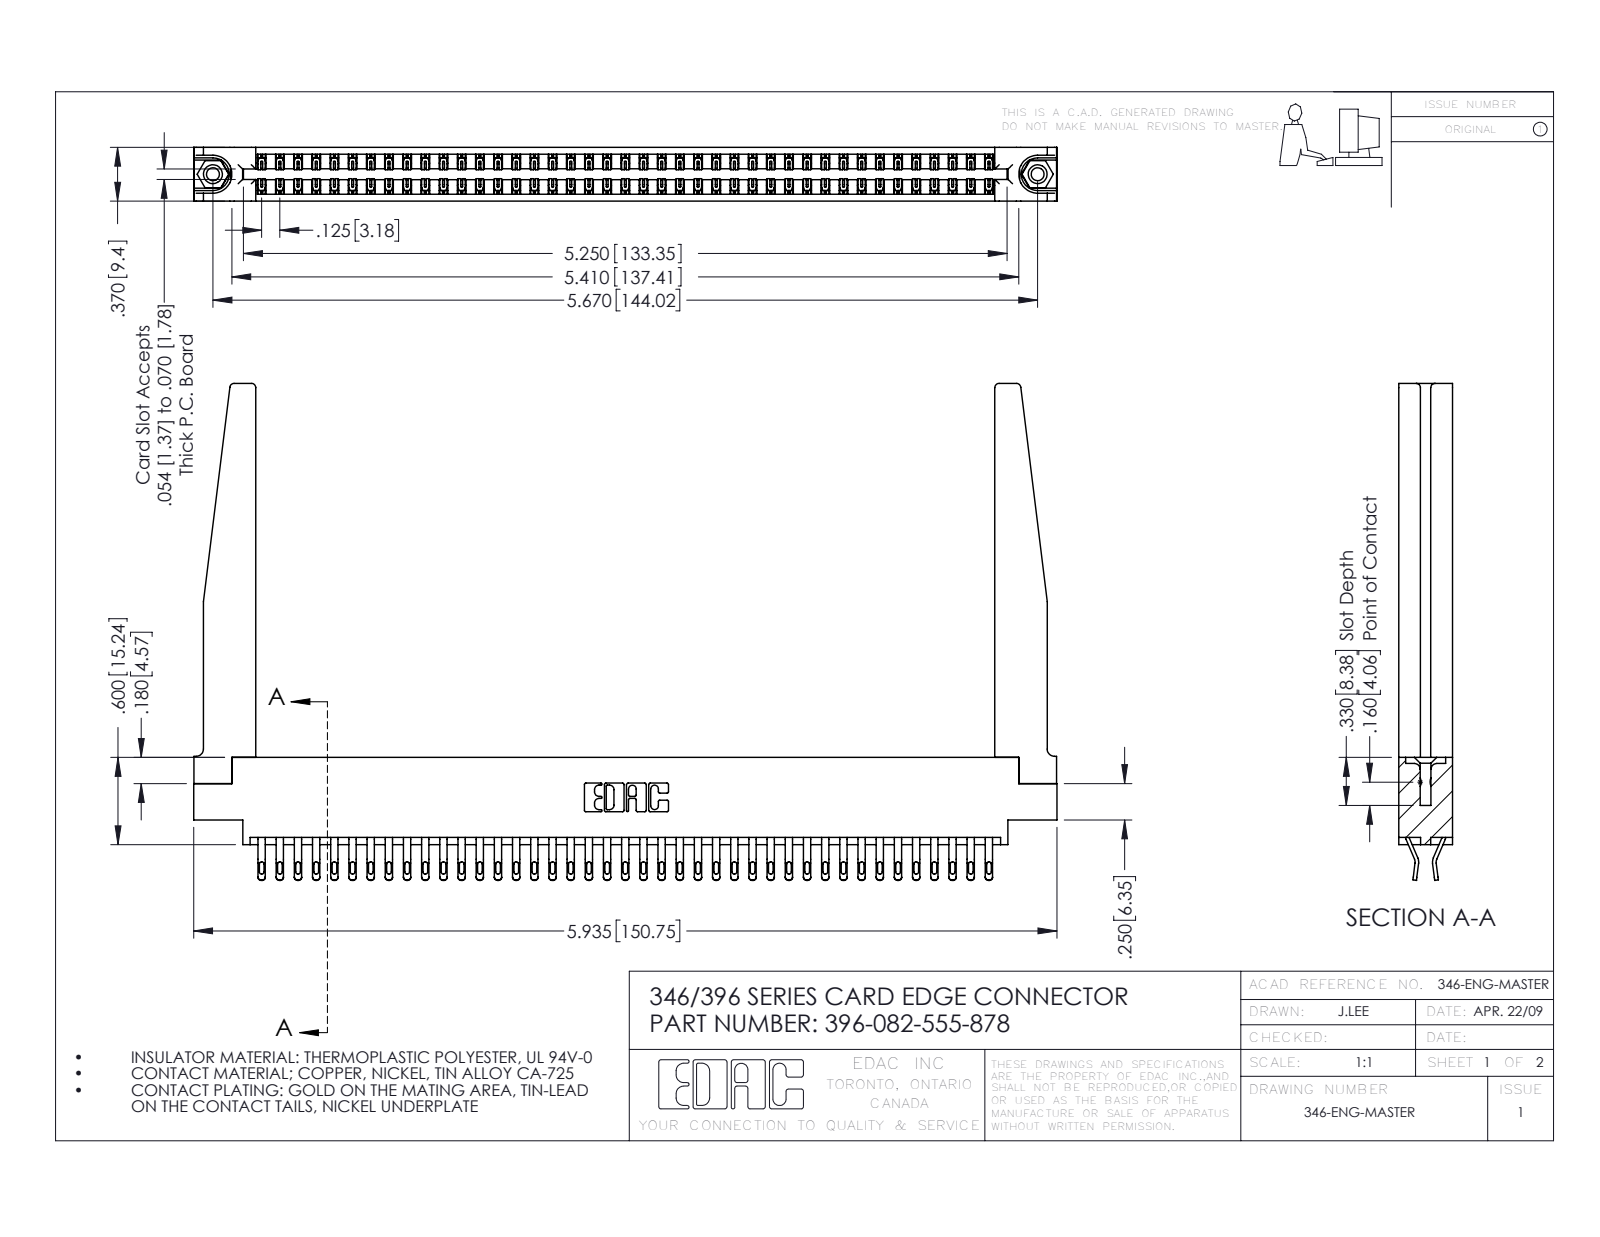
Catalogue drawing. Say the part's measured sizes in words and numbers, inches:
The part is named "345-292-001_555 Tail; 346-220-078_345-220-078; 346 Part_0.170 Offset - 0.156 Dia-TH; 396-082-555-878 (+1 more)". Its 3-D file was written by "SolidWorks 2016 (CONFIG_CONTROL_DESIGN)". It is 87 solids with 5116 faces: 2928 planar, 2136 cylindrical and 52 other. Overall it measures 5.935 by 3.415 by 0.37 inches. Its volume is 1.323 cubic inches and its surface area 43.18 square inches. Round holes: 2 of diameter 0.089, 2 of diameter 0.125, 2 of diameter 0.156, 1 of diameter 0.064. Round bosses or shafts: 2 of diameter 0.155. Partial cylindrical surfaces (rounded edges, fillets, slot ends): 164 of radius 0.016, 164 of radius 0.02, 123 of radius 0.006, 22 of radius 0.01, 8 of radius 0.03, 6 of radius 0.007, 6 of radius 0.031, 4 of radius 0.05. The main face-to-face distances are 0.37, 0.048, 0.322, 0.072, 0.15, 0.148, 0.25, 0.025, 0.298, 0.275. The hole center spacings are 0.246, 5.461, 5.67.
